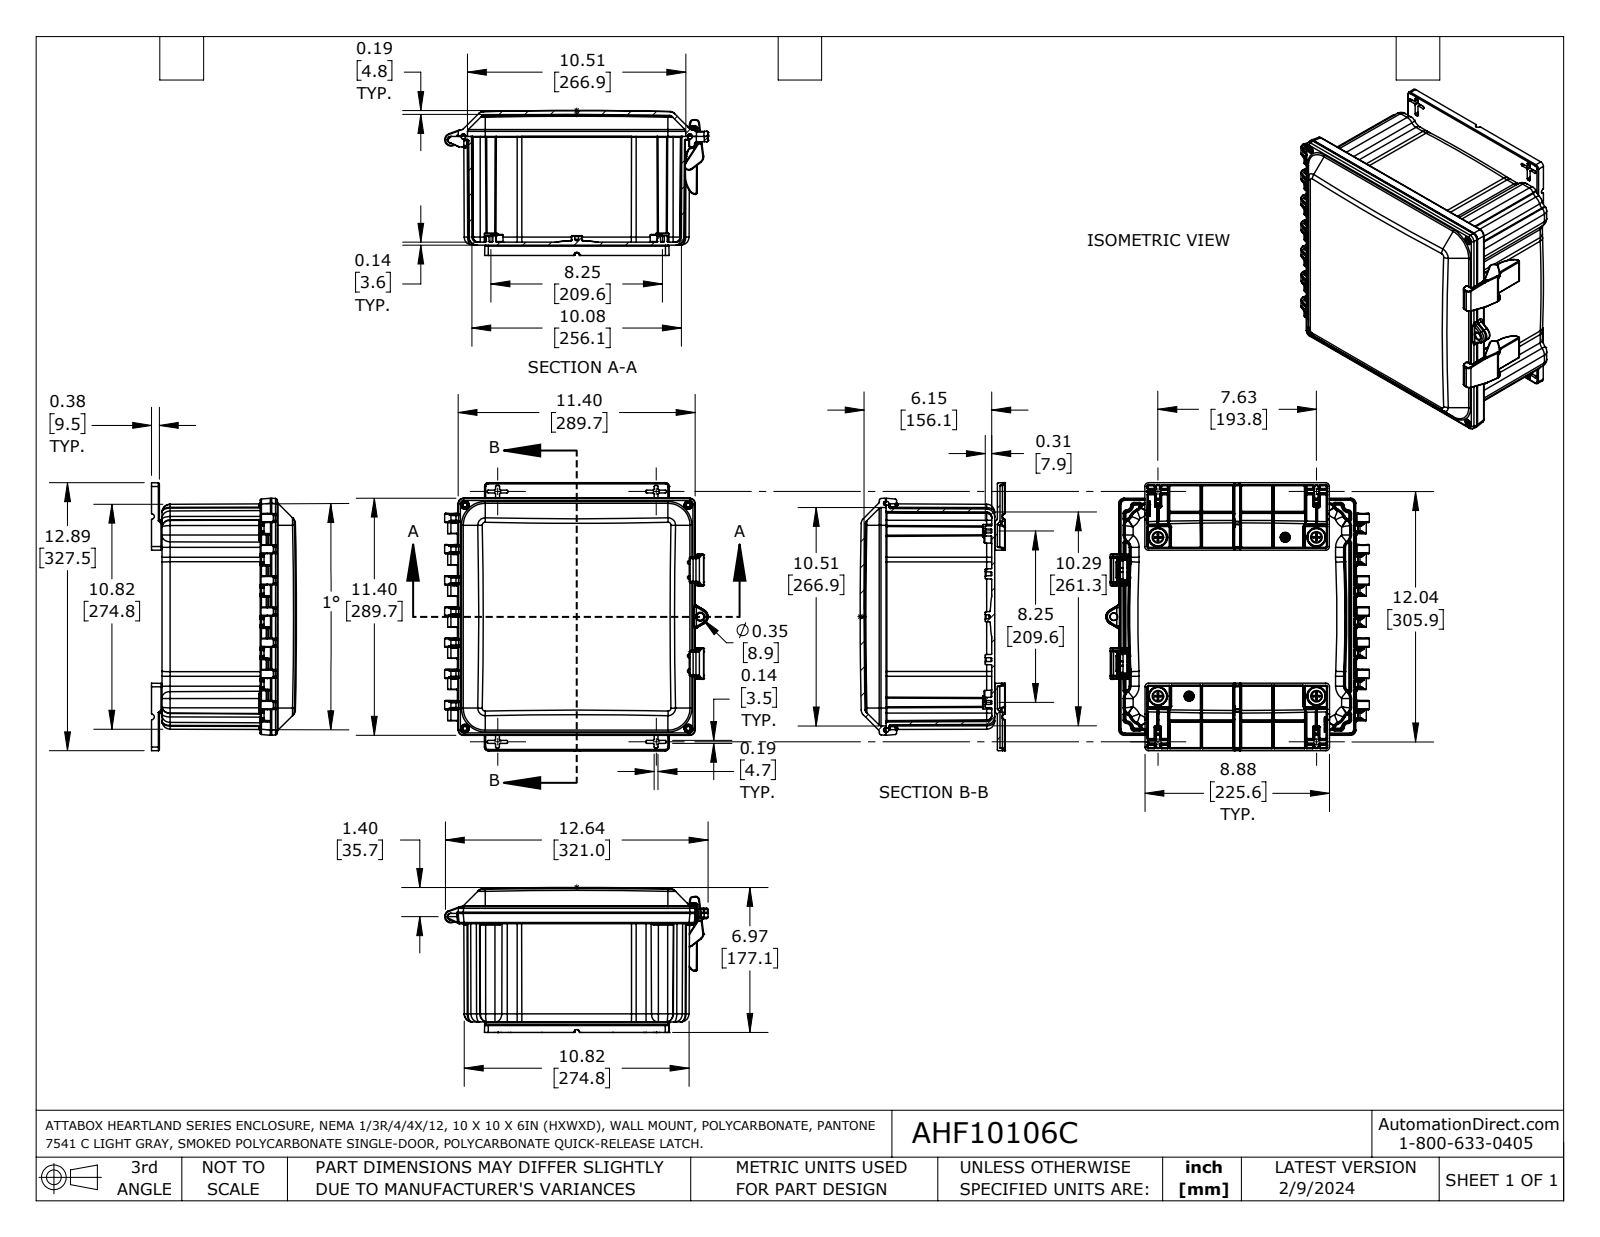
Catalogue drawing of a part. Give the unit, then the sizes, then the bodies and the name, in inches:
Units: inches
Overall size (bounding box): 12.892 × 12.676 × 6.973
Round holes (diameter × count): ⌀0.187 ×11, ⌀0.195 ×4, ⌀0.25 ×4, ⌀0.26 ×4, ⌀0.27 ×4, ⌀0.323 ×4, ⌀0.39 ×4, ⌀0.327 ×1, ⌀0.375 ×1, ⌀0.45 ×1
Round bosses / shafts (diameter × count): ⌀0.487 ×11, ⌀0.625 ×4, ⌀0.25 ×4, ⌀0.2 ×2, ⌀0.313 ×1
Partial cylindrical surfaces — rounded edges, fillets, slot ends (radius × count): R0.035 ×184, R0.065 ×27, R0.01 ×22, R0.02 ×21, R0.334 ×16, R0.05 ×8, R0.417 ×8, R0.095 ×6
Main face-to-face distances: 0.119, 10.119, 0.14, 10, 0.5, 5.225, 10.238, 0.64, 5.725, 5.085
Hole centre spacings: 4.125, 4.125, 5.833, 9.582, 3.825, 4.612, 7.633, 8.504
Volume: 114.8 in³ · Surface area: 1 264 in²
Bodies: 12 solids, 1736 faces (590 planar, 519 cylindrical, 627 other)
Part name (STEP PRODUCT): AHF10106C
STEP written by: SolidWorks 2023 (AUTOMOTIVE_DESIGN)
